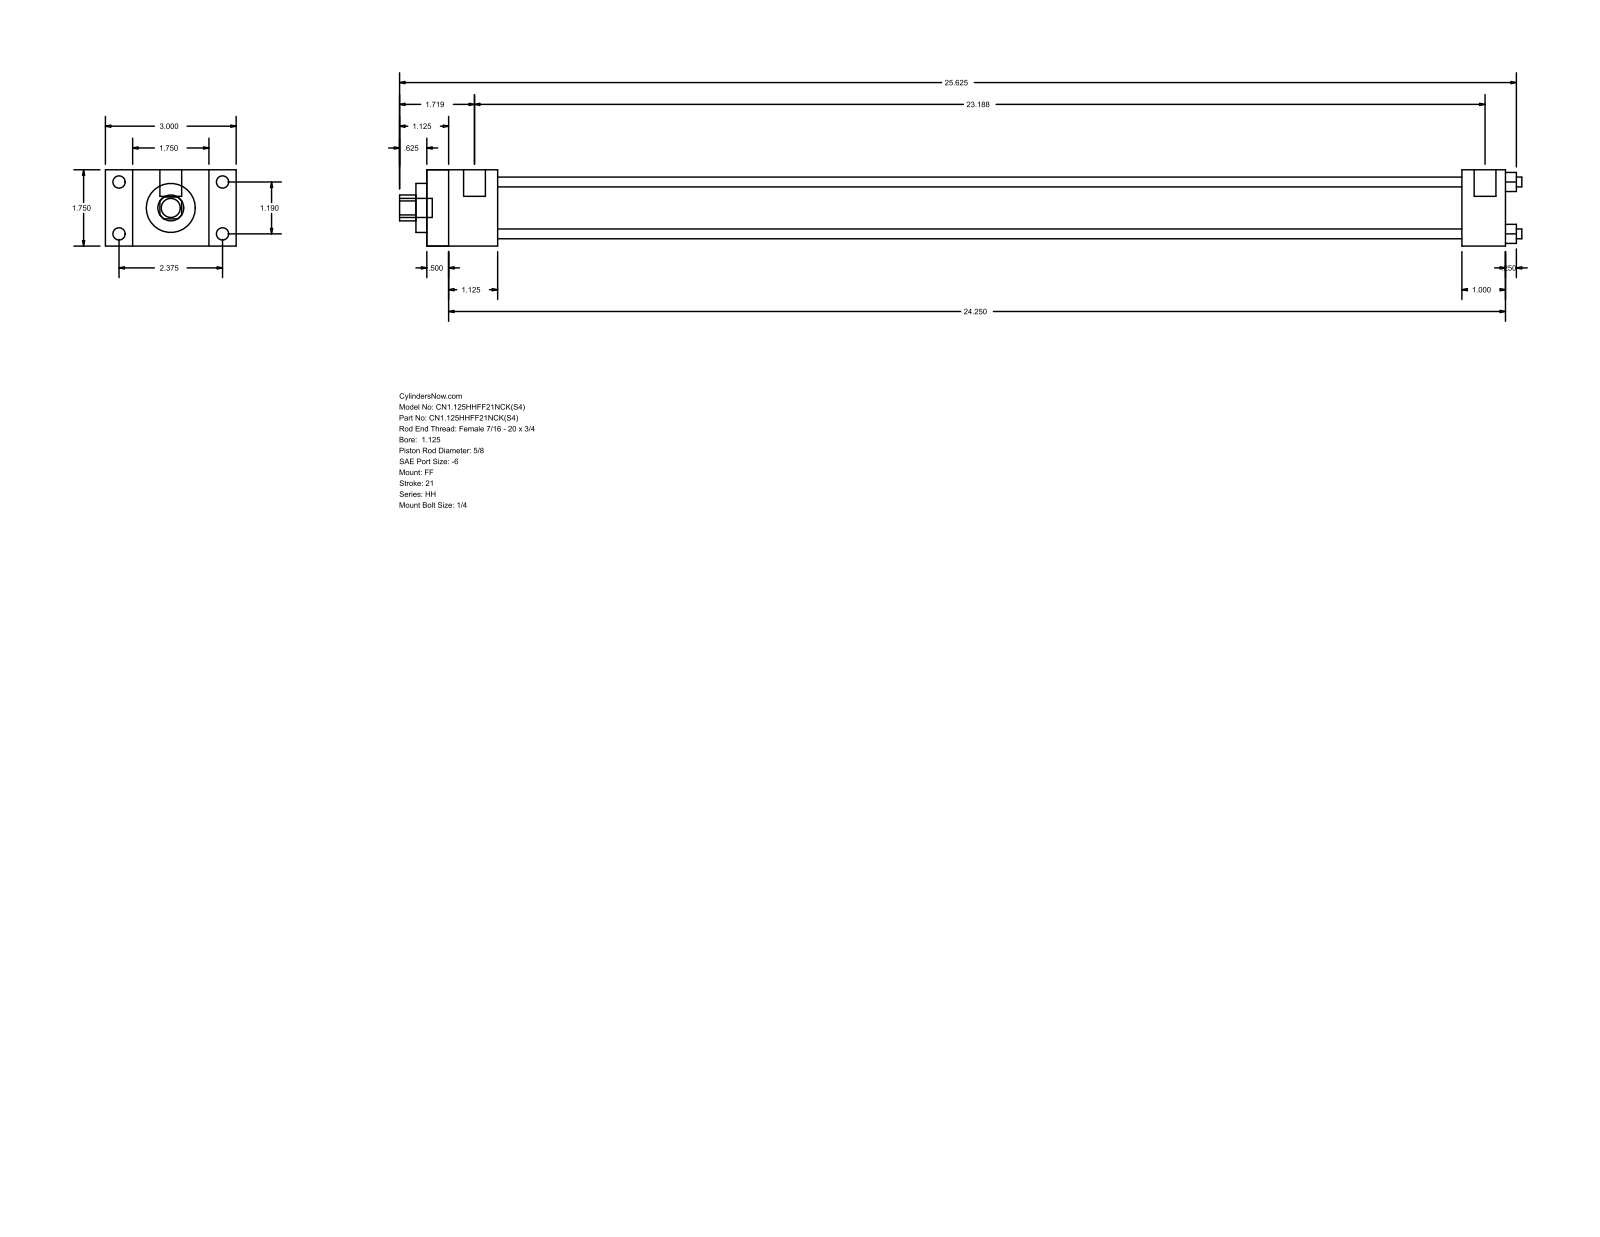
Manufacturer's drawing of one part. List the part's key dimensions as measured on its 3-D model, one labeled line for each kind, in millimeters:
Part name (STEP PRODUCT): HH_FF__0112_0.625
STEP written by: GSSL Pune (CONFIG_CONTROL_DESIGN)
Units: millimetres
Bodies: 0 solids, 92 faces (64 planar, 28 cylindrical, 0 other)
Overall size (bounding box): 654.05 × 76.2 × 44.45
Round holes (diameter × count): ⌀5.71 ×4, ⌀15.88 ×1, ⌀28.57 ×1, ⌀34.92 ×1
Round bosses / shafts (diameter × count): ⌀7.14 ×4, ⌀5.56 ×4, ⌀12.7 ×2, ⌀11.11 ×1
Partial cylindrical surfaces — rounded edges, fillets, slot ends (radius × count): R7.54 ×1
Main face-to-face distances: 44.46, 628.64, 15.87, 12.69, 615.95, 60.33, 28.58, 41.27, 603.24, 590.55
Hole centre spacings: 21.37, 30.22, 42.74
